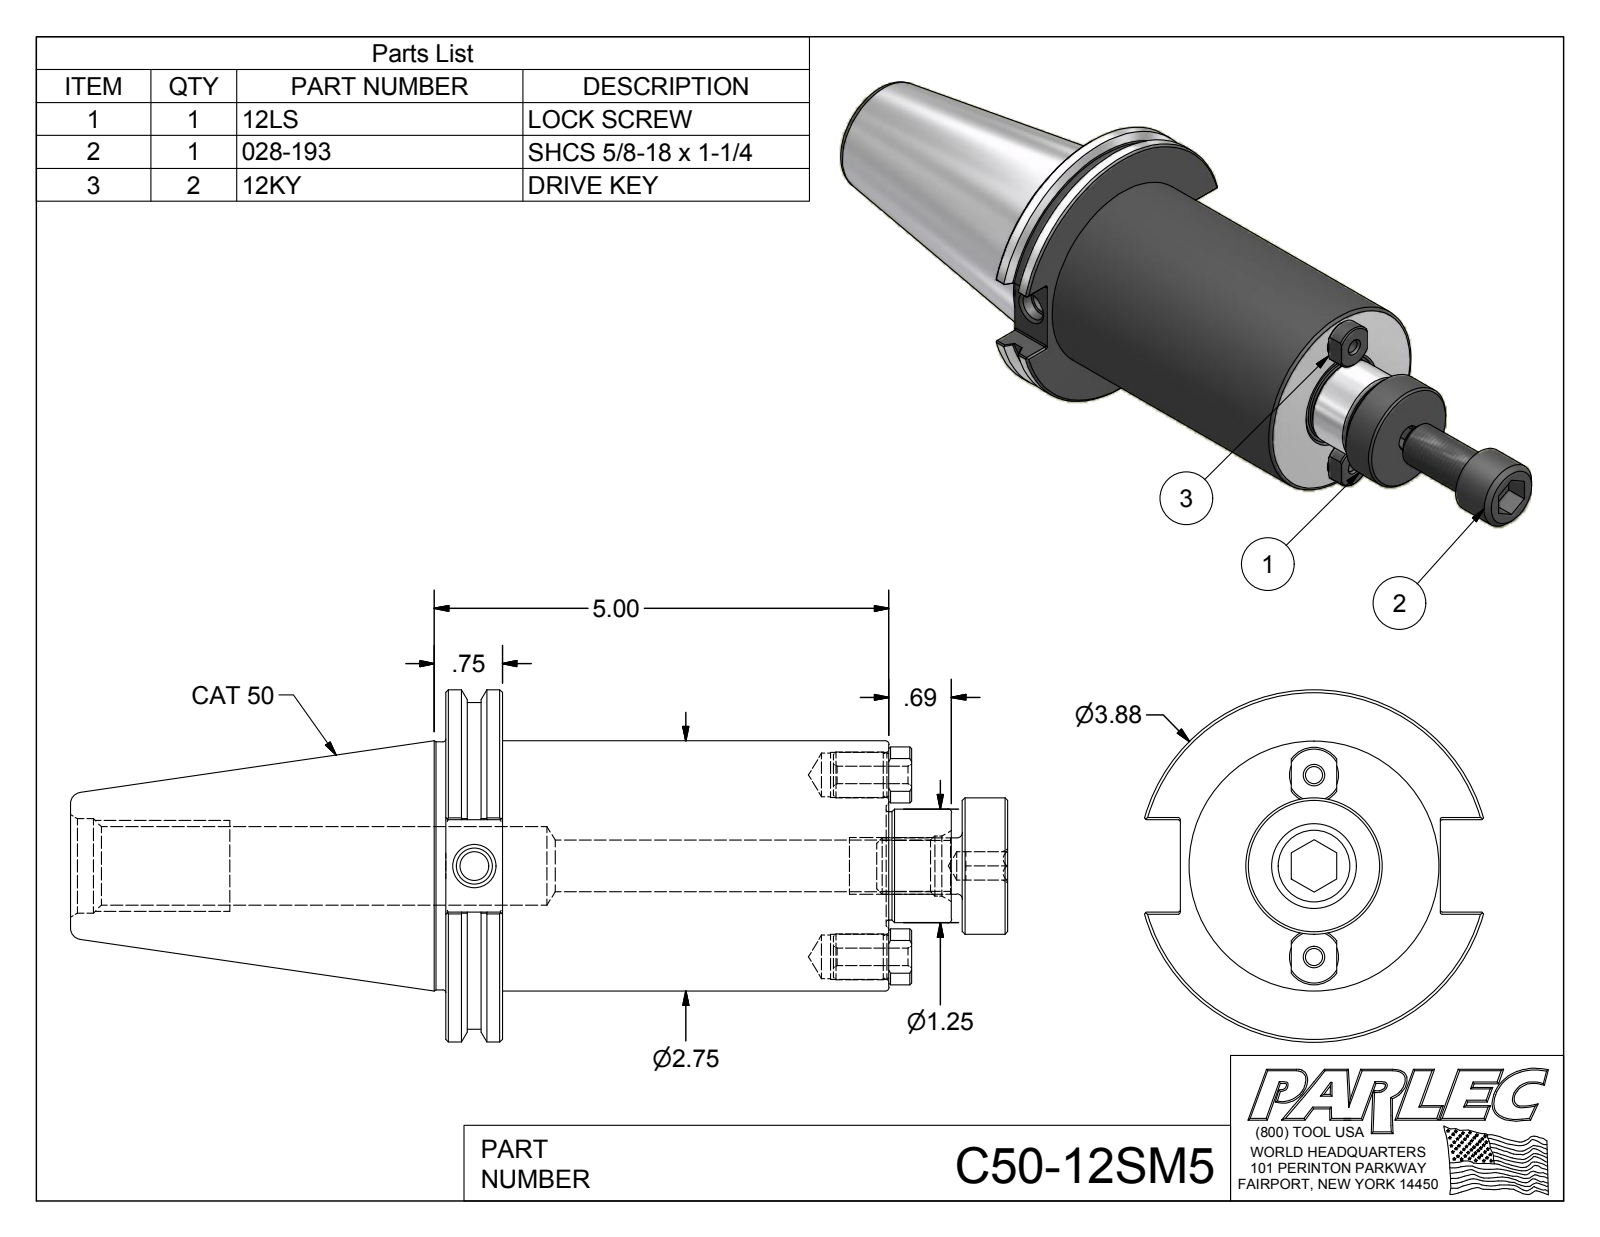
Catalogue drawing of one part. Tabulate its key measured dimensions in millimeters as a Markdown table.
| quantity | value |
| --- | --- |
| part name | C50-12SM5; C50-12SM5-1; 12KY; 12LS (+1 more) |
| STEP written by | Autodesk Inventor 2012 (AUTOMOTIVE_DESIGN) |
| units | millimeters |
| bodies | 5 solids, 172 faces (67 planar, 47 cylindrical, 58 other) |
| overall size | 312.6 × 98.4 × 94.7 |
| volume | 751 300 mm³ |
| surface area | 89 290 mm² |
| round holes (diameter × count) | 4.8 × 2, 12.2 × 2, 12.7 × 2, 7.9 × 1, 8 × 1, 10.1 × 1, 14.4 × 1, 16.8 × 1, 22 × 1, 26.4 × 1 |
| round bosses / shafts (diameter × count) | 12.8 × 2, 11.9 × 2, 98.4 × 1, 91.3 × 1, 69.9 × 1, 69.3 × 1, 38.1 × 1, 31.8 × 1 |
| partial cylindrical surfaces (radius × count) | 0.5 × 12, 7.8 × 2 |
| main face-to-face distances | 15.9, 123.8, 108, 157, 141.1, 33.2, 12.7, 144.3, 128.4, 20.5 |
| hole center spacings | 25.4, 50.8 |
